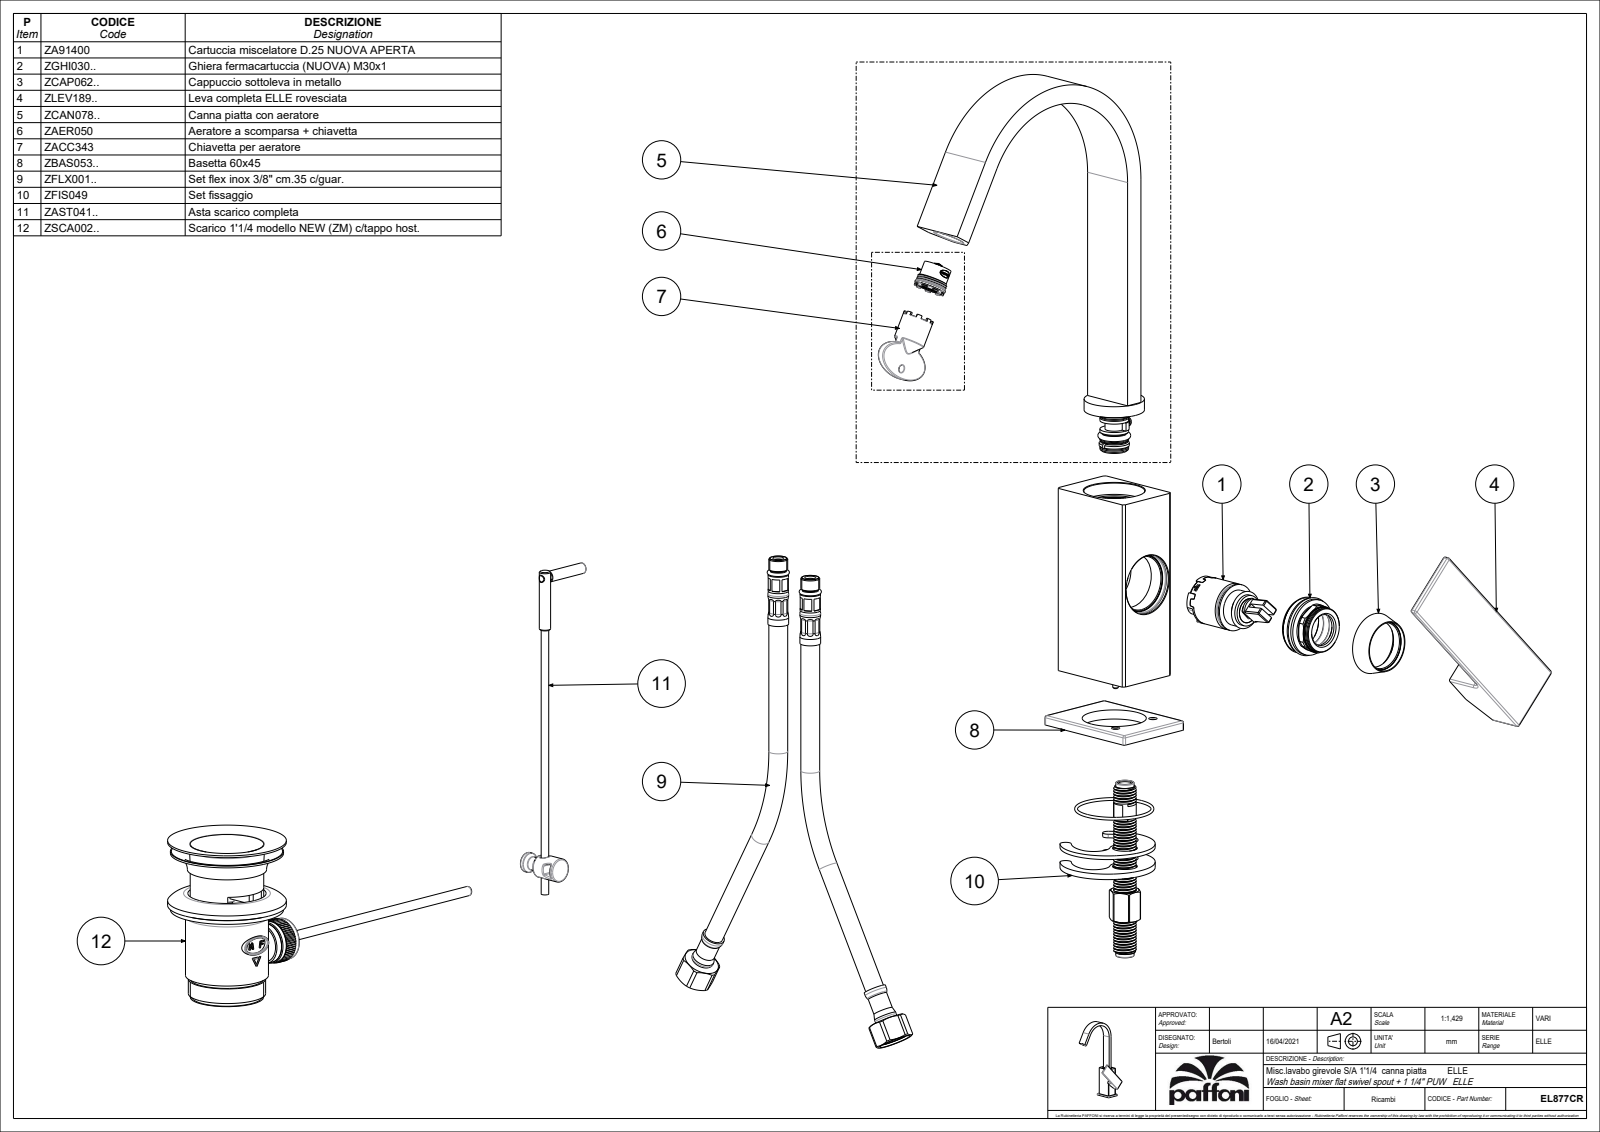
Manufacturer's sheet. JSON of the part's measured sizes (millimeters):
{"part_name": "EL877CR", "step_written_by": "CREO PARAMETRIC BY PTC INC, 2020044 (CONFIG_CONTROL_DESIGN)", "units": "millimeters", "bodies": {"solids": 1, "faces": 386, "planar": 112, "cylindrical": 167, "other": 107}, "overall_size": [290.2, 160.93, 83.28], "volume_mm3": 282100, "surface_area_mm2": 82605, "round_holes": [[4.5, 3], [6, 3], [7, 3], [3, 2], [3.2, 2], [5, 2], [5.5, 2], [9, 2], [11, 2], [3.3, 1], [4, 1], [8, 1]], "round_bosses_or_shafts": [[38.8, 1], [32, 1], [20, 1], [15.2, 1], [12, 1], [11.2, 1], [9.8, 1], [8.8, 1]], "partial_cylinders_radius": [[1, 21], [1.5, 8], [3, 2], [5, 1], [30, 1], [52.49, 1], [62.49, 1]], "face_to_face_distances": [10, 23, 13, 36, 40, 30, 38.28, 78.28, 68.28, 4], "hole_center_spacings": [6.72, 8.95, 9.34, 9.43, 10.12, 11.2, 11.31, 15.26]}
